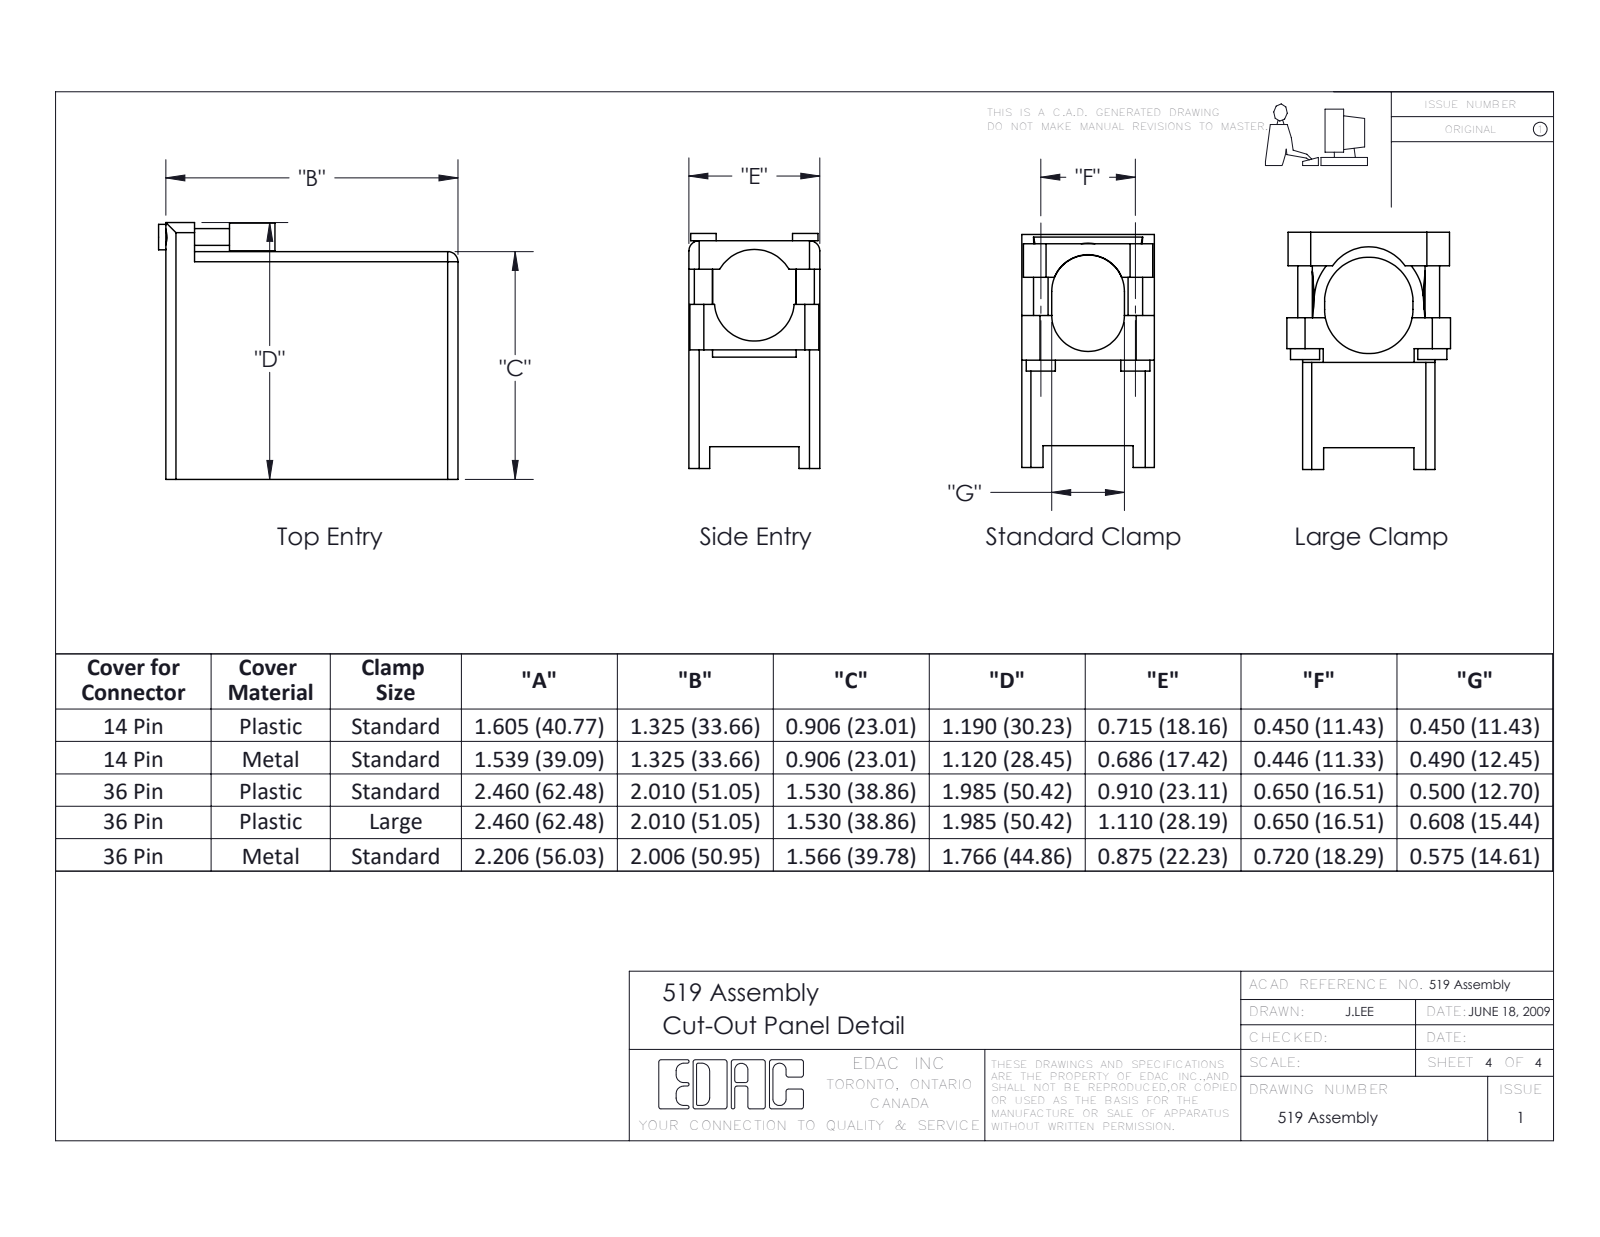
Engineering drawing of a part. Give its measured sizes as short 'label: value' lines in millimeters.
name: 516-252-025-100_516-252-025-100; 516-230-001_Plastic - 020 Side Entry; 519-014-000-426; 519 Receptacle Insulator_014
written by: SolidWorks 2020 (CONFIG_CONTROL_DESIGN)
unit: mm
bodies: 3 solids, 595 faces (363 planar, 216 cylindrical, 16 other)
size: 40.9 × 37.5 × 20.2
volume: 10 000 mm³; area: 13 270 mm²
holes: 14× ⌀3.3, 7× ⌀2.4, 2× ⌀3, 1× ⌀1.8, 1× ⌀2.7, 1× ⌀3.3, 1× ⌀4.3, 1× ⌀5.2, 1× ⌀11.5
bosses: 3× ⌀3.2, 2× ⌀2
rounds: 22× R0.3, 10× R1, 9× R1.2, 8× R0.8, 6× R0.2, 6× R0.8, 5× R2.3, 4× R0.3
face distances: 1.2, 16.9, 18.2, 15.7, 8.1, 2.7, 5.4, 0.8, 1.4, 16.7
hole spacings: 3.8, 7.6, 8.5, 5.4, 8.5, 11.4, 4.3, 5.3
